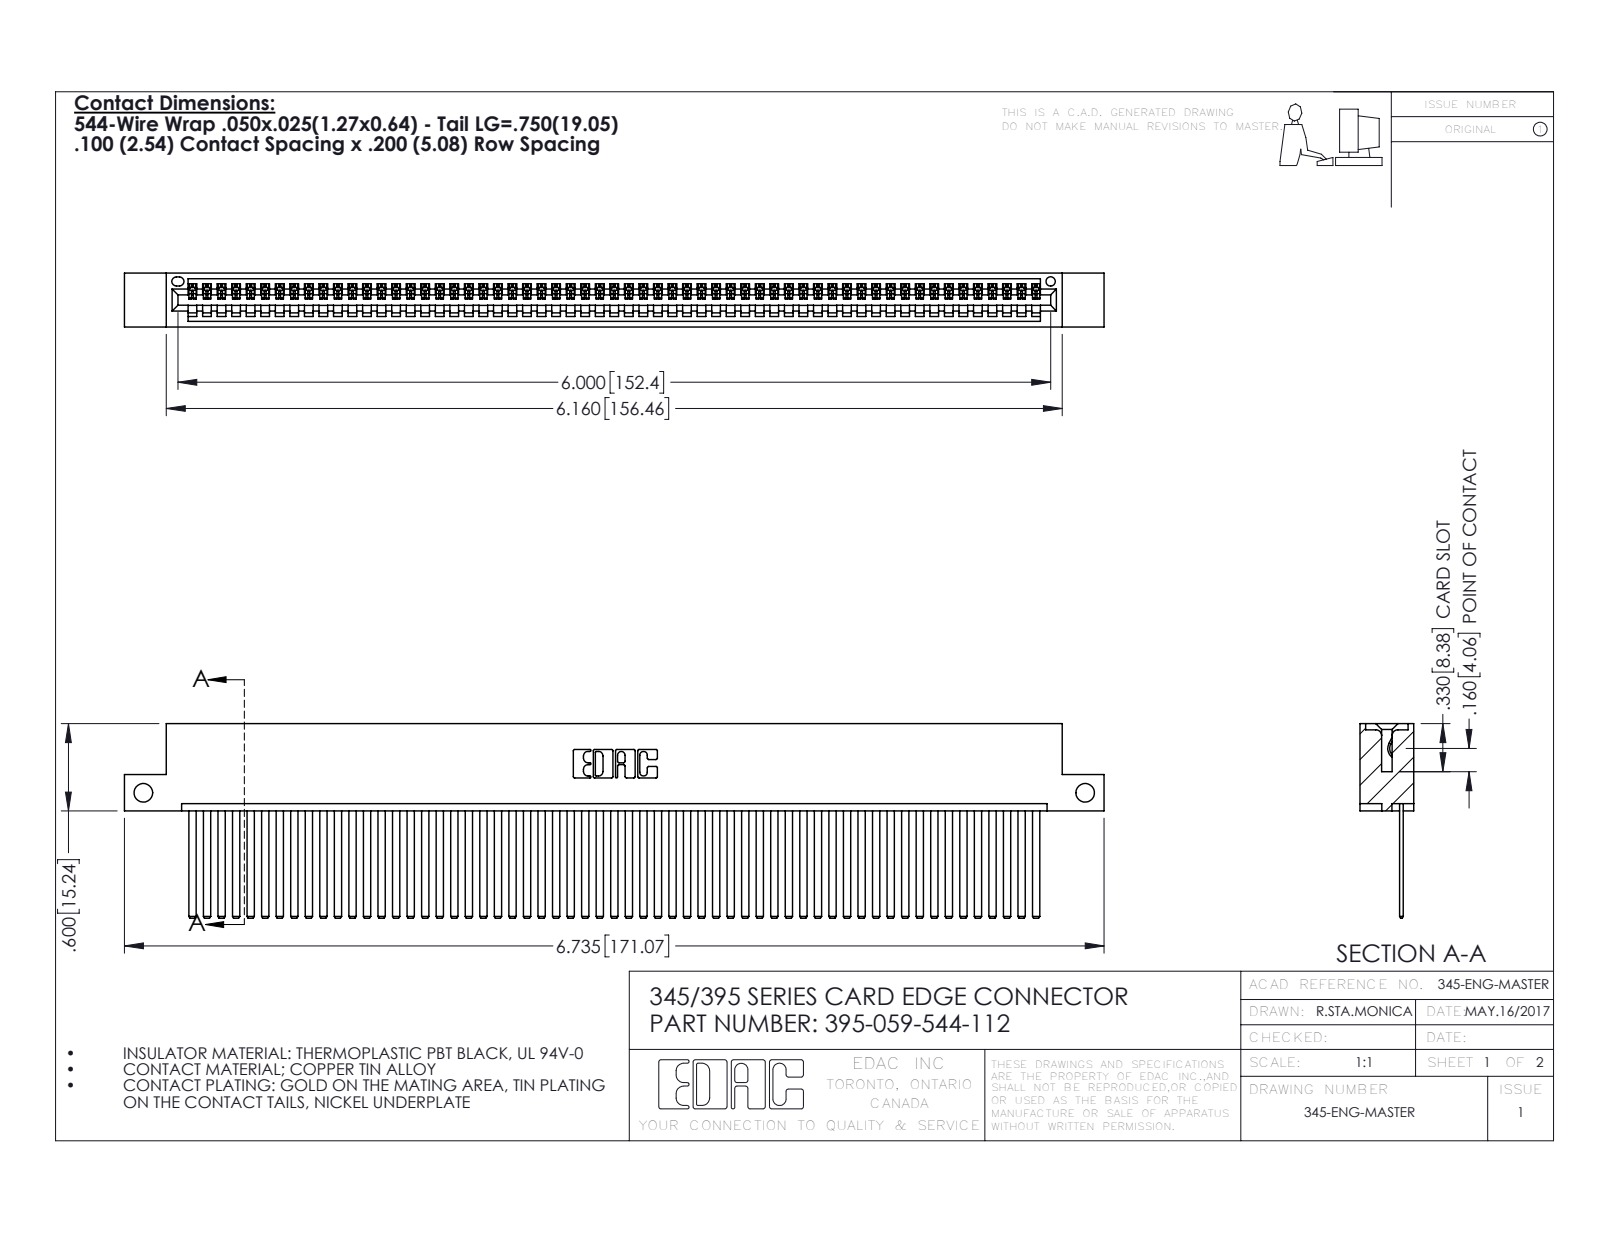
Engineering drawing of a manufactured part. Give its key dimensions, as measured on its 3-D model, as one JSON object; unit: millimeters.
{"part_name": "345-292-001_345-293-144; 345 Part_Flush Mounting Lugs - Side Mount; 395-059-544-112", "step_written_by": "SolidWorks 2016 (CONFIG_CONTROL_DESIGN)", "units": "millimeters", "bodies": {"solids": 60, "faces": 3194, "planar": 2204, "cylindrical": 990, "other": 0}, "overall_size": [171.1, 34, 9.4], "volume_mm3": 16980, "surface_area_mm2": 24710, "round_holes": [[3.3, 2], [1.6, 1]], "partial_cylinders_radius": [[0.2, 118], [0.3, 22], [0.2, 6], [0.8, 6], [0.7, 3], [0.8, 2], [1, 2], [0.4, 1]], "face_to_face_distances": [1.8, 7.6, 0.6, 2.5, 6.9, 9.4, 5.1, 5.7, 3.8, 1.8], "hole_center_spacings": [164.5]}
